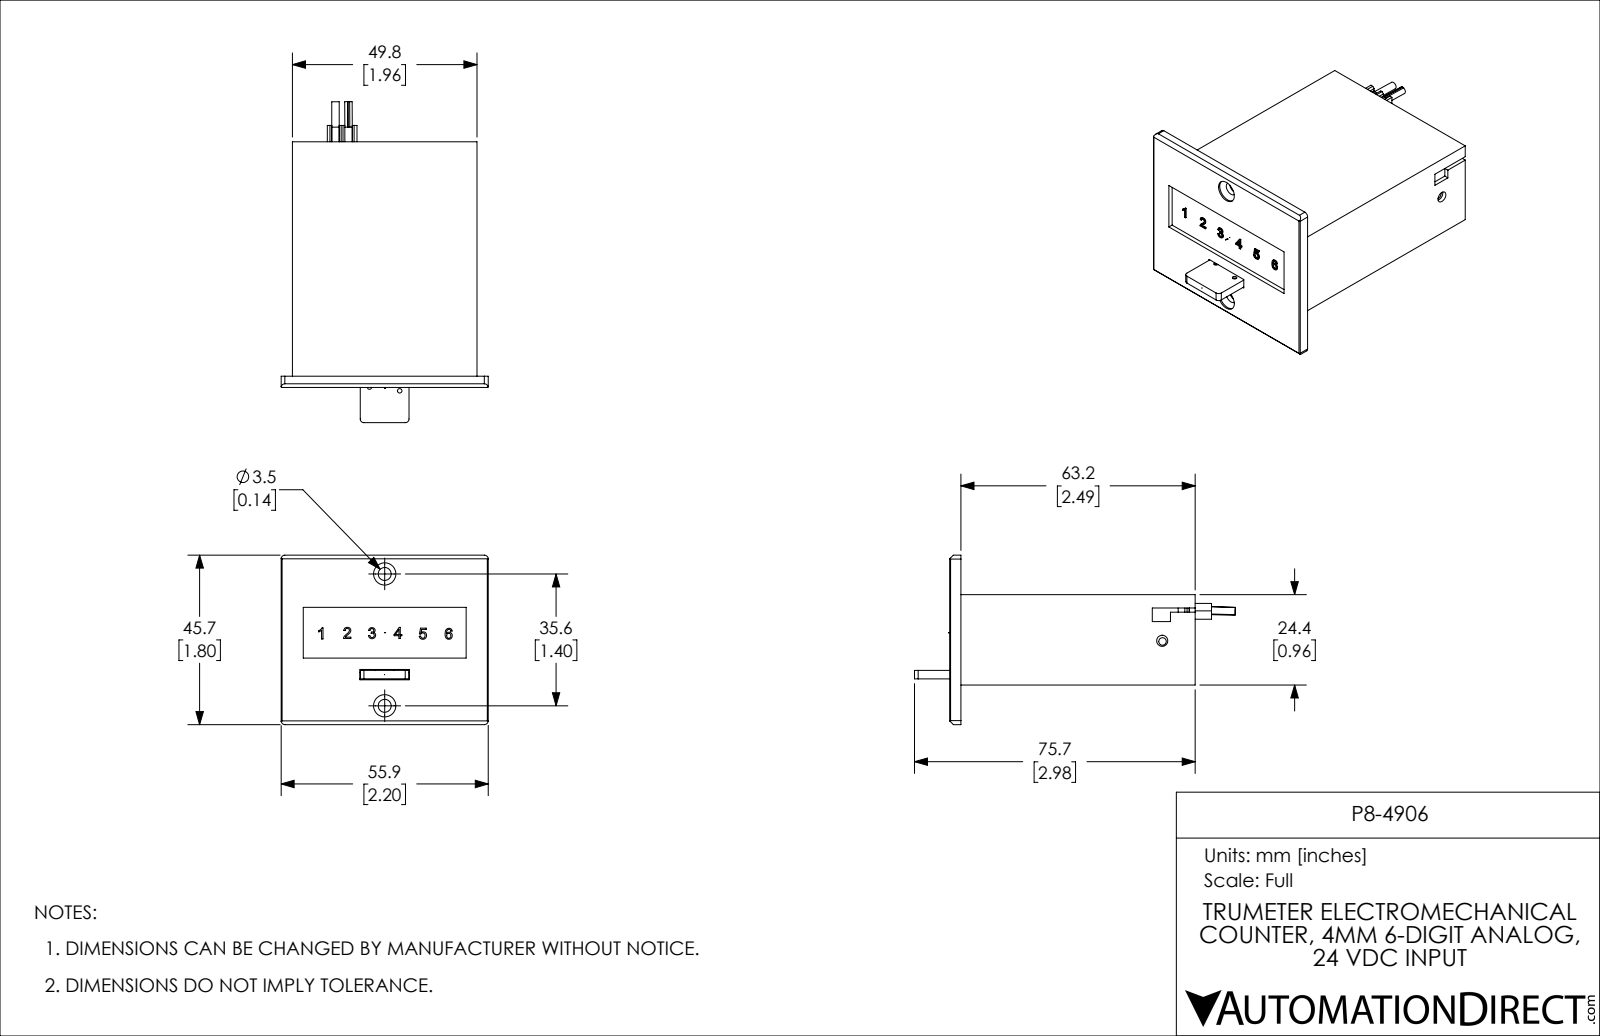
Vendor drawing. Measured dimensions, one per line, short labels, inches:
name: P8-4906
written by: SolidWorks 2021 (CONFIG_CONTROL_DESIGN)
unit: in
bodies: 4 solids, 433 faces (292 planar, 98 cylindrical, 43 other)
size: 3.409 × 2.2 × 1.8
volume: 1.42 in³; area: 50.16 in²
holes: 5× ⌀0.08, 2× ⌀0.047, 2× ⌀0.098, 2× ⌀0.138, 2× ⌀0.236, 1× ⌀0.072, 1× ⌀0.08, 1× ⌀0.118, 1× ⌀0.123
bosses: 2× ⌀0.079
rounds: 9× R0.039, 5× R0.012, 3× R0.079, 2× R0.006, 2× R0.01, 2× R0.042, 2× R0.05, 2× R0.063
face distances: 0.05, 0.063, 0.96, 0.91, 0.118, 1.842, 0.055, 1.905, 1.787, 0.12
hole spacings: 0.093, 0.191, 0.323, 0.331, 0.363, 0.394, 0.413, 0.445
